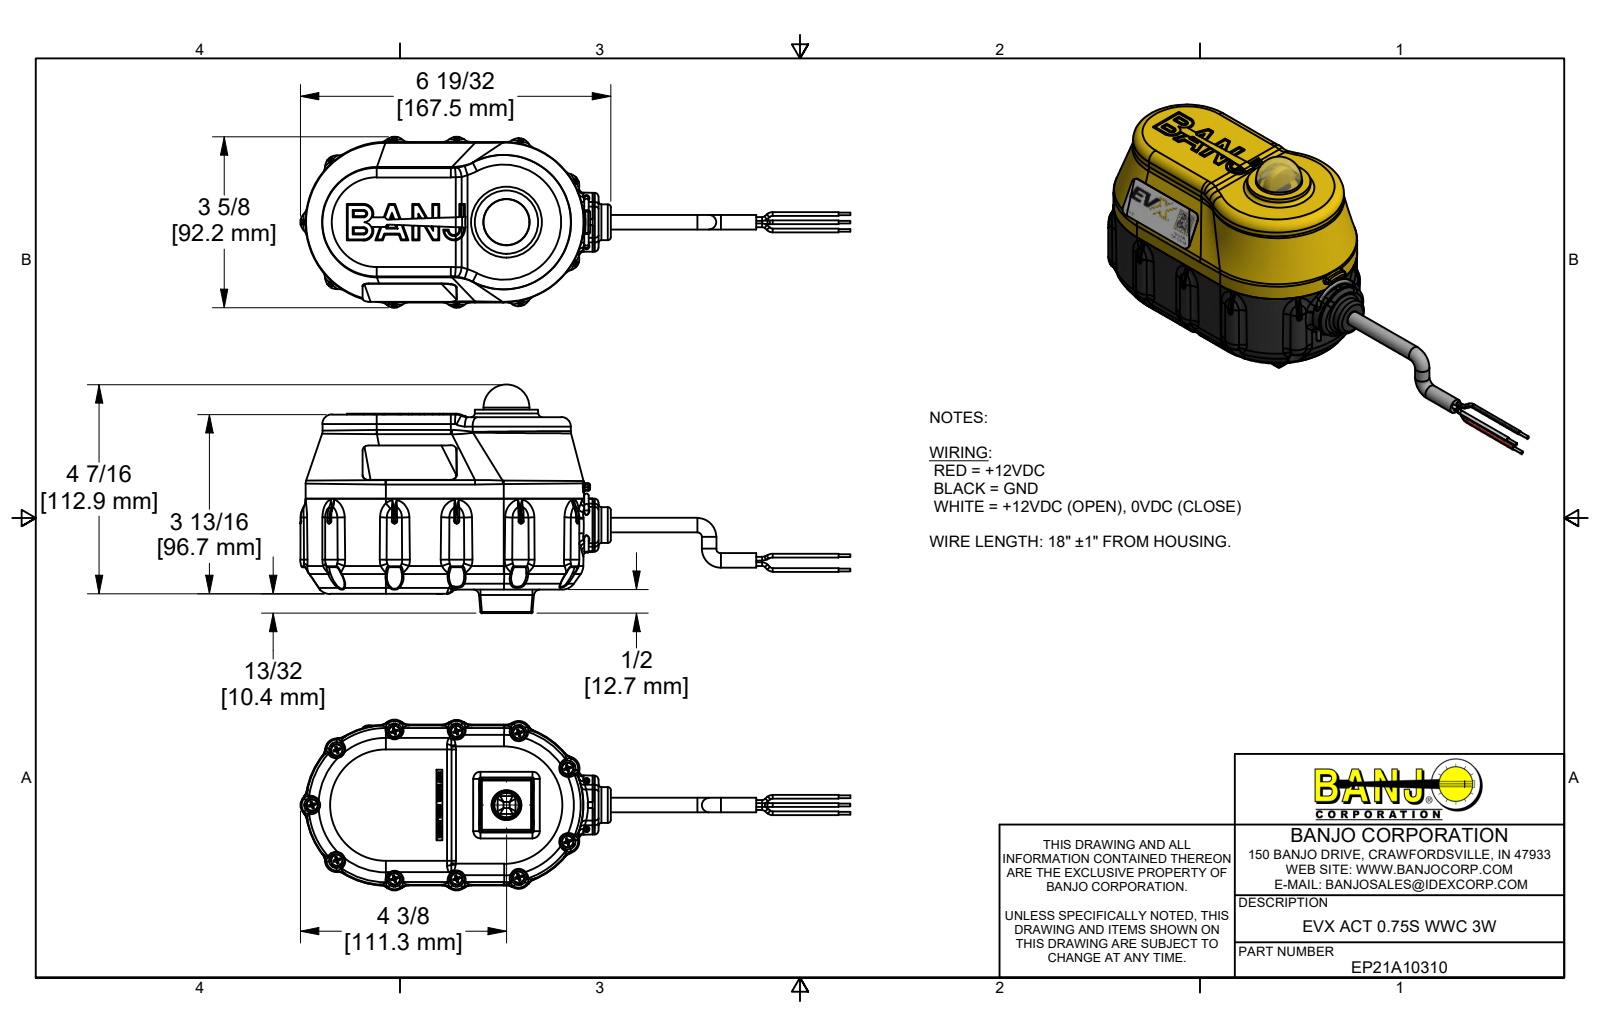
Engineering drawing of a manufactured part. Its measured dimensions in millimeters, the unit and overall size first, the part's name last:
Units: millimetres
Overall size (bounding box): 296.8 × 123.3 × 92.2
Round holes (diameter × count): ⌀2.4 ×11, ⌀3.8 ×11, ⌀2 ×7, ⌀2.7 ×4, ⌀3.2 ×4, ⌀3.5 ×4, ⌀3.8 ×4, ⌀3.8 ×4, ⌀4.3 ×4, ⌀2.7 ×2, ⌀3 ×2, ⌀3.1 ×2
Round bosses / shafts (diameter × count): ⌀6.4 ×17, ⌀2 ×15, ⌀3.6 ×11, ⌀2.7 ×11, ⌀2.2 ×11, ⌀1.5 ×6, ⌀6.9 ×4, ⌀5.6 ×4
Partial cylindrical surfaces — rounded edges, fillets, slot ends (radius × count): R0.3 ×180, R1 ×145, R0.3 ×84, R0.5 ×71, R0.1 ×54, R2 ×28, R0.8 ×26, R0.4 ×22
Main face-to-face distances: 2.5, 65.2, 5.4, 1.5, 3.8, 48.2, 42.8, 46.6, 62.6, 19.8
Hole centre spacings: 32.6, 38.4, 68.3, 72.4, 96.2, 12.4, 17, 31.1
Volume: 510 800 mm³ · Surface area: 261 300 mm²
Bodies: 73 solids, 10011 faces (2568 planar, 2938 cylindrical, 4505 other)
Part name (STEP PRODUCT): EP21A10310; EP10310; IRF4905; optical sensor (+8 more)
STEP written by: Autodesk Inventor 2019 (AUTOMOTIVE_DESIGN)
